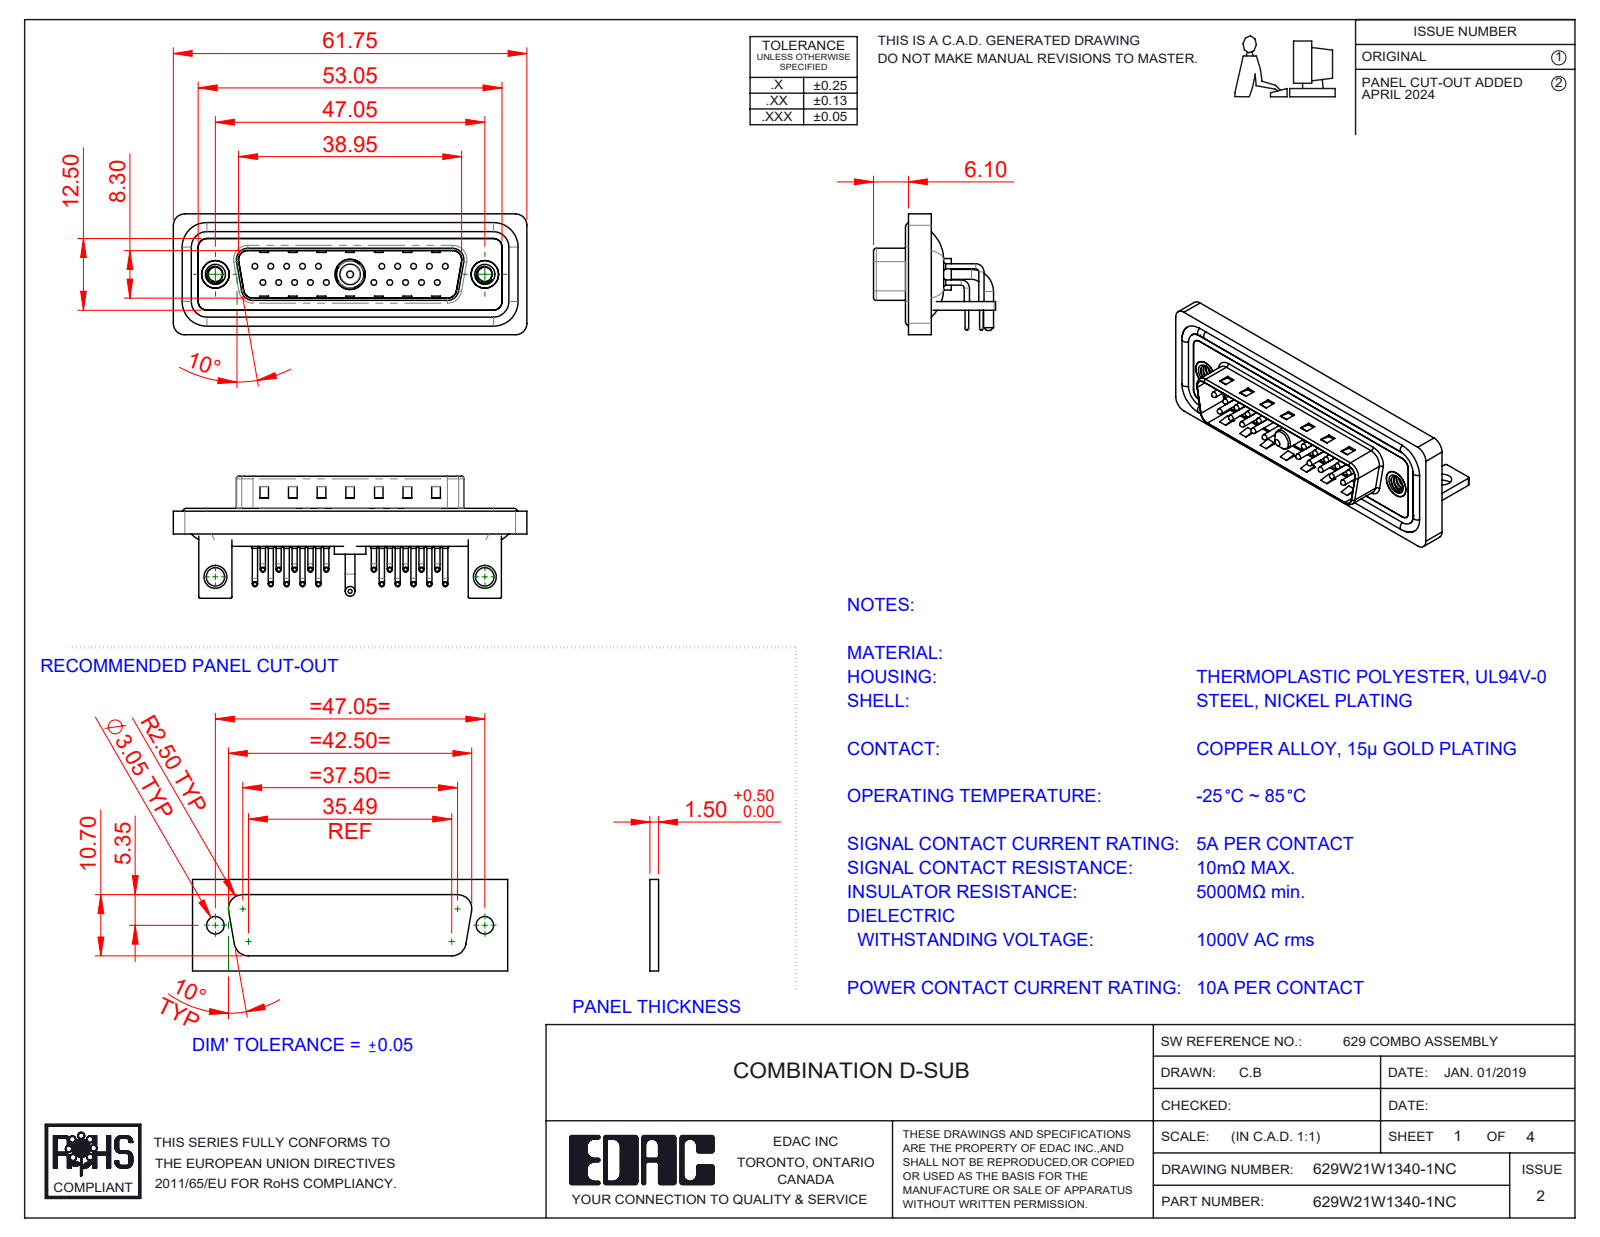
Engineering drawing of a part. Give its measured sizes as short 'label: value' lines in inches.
name: 629Combo Threaded Rivet_B; Power Pin_10A RA; 629Combo Waterproof Housing_25 Contacts; 629Combo Shell Rear_25 Contacts (+6 more)
written by: SolidWorks 2023 (CONFIG_CONTROL_DESIGN)
unit: in
bodies: 31 solids, 2764 faces (1519 planar, 947 cylindrical, 298 other)
size: 2.431 × 0.839 × 0.831
volume: 0.466 in³; area: 20.55 in²
holes: 20× ⌀0.03, 20× ⌀0.063, 20× ⌀0.079, 2× ⌀0.098, 2× ⌀0.126, 2× ⌀0.157, 2× ⌀0.189, 2× ⌀0.197, 1× ⌀0.191, 1× ⌀0.209
bosses: 40× ⌀0.035, 20× ⌀0.059, 20× ⌀0.039, 20× ⌀0.026, 4× ⌀0.063, 2× ⌀0.193, 2× ⌀0.067, 1× ⌀0.217
rounds: 20× R0.04, 19× R0.079, 18× R0.059, 16× R0.01, 9× R0.02, 8× R0.063, 4× R0.024, 4× R0.026
face distances: 0.016, 0.031, 0.083, 0.114, 0.059, 0.043, 0.161, 0.063, 0.177, 0.146
hole spacings: 0.124, 0.109, 0.218, 0.327, 0.198, 0.763, 0.826, 0.872
